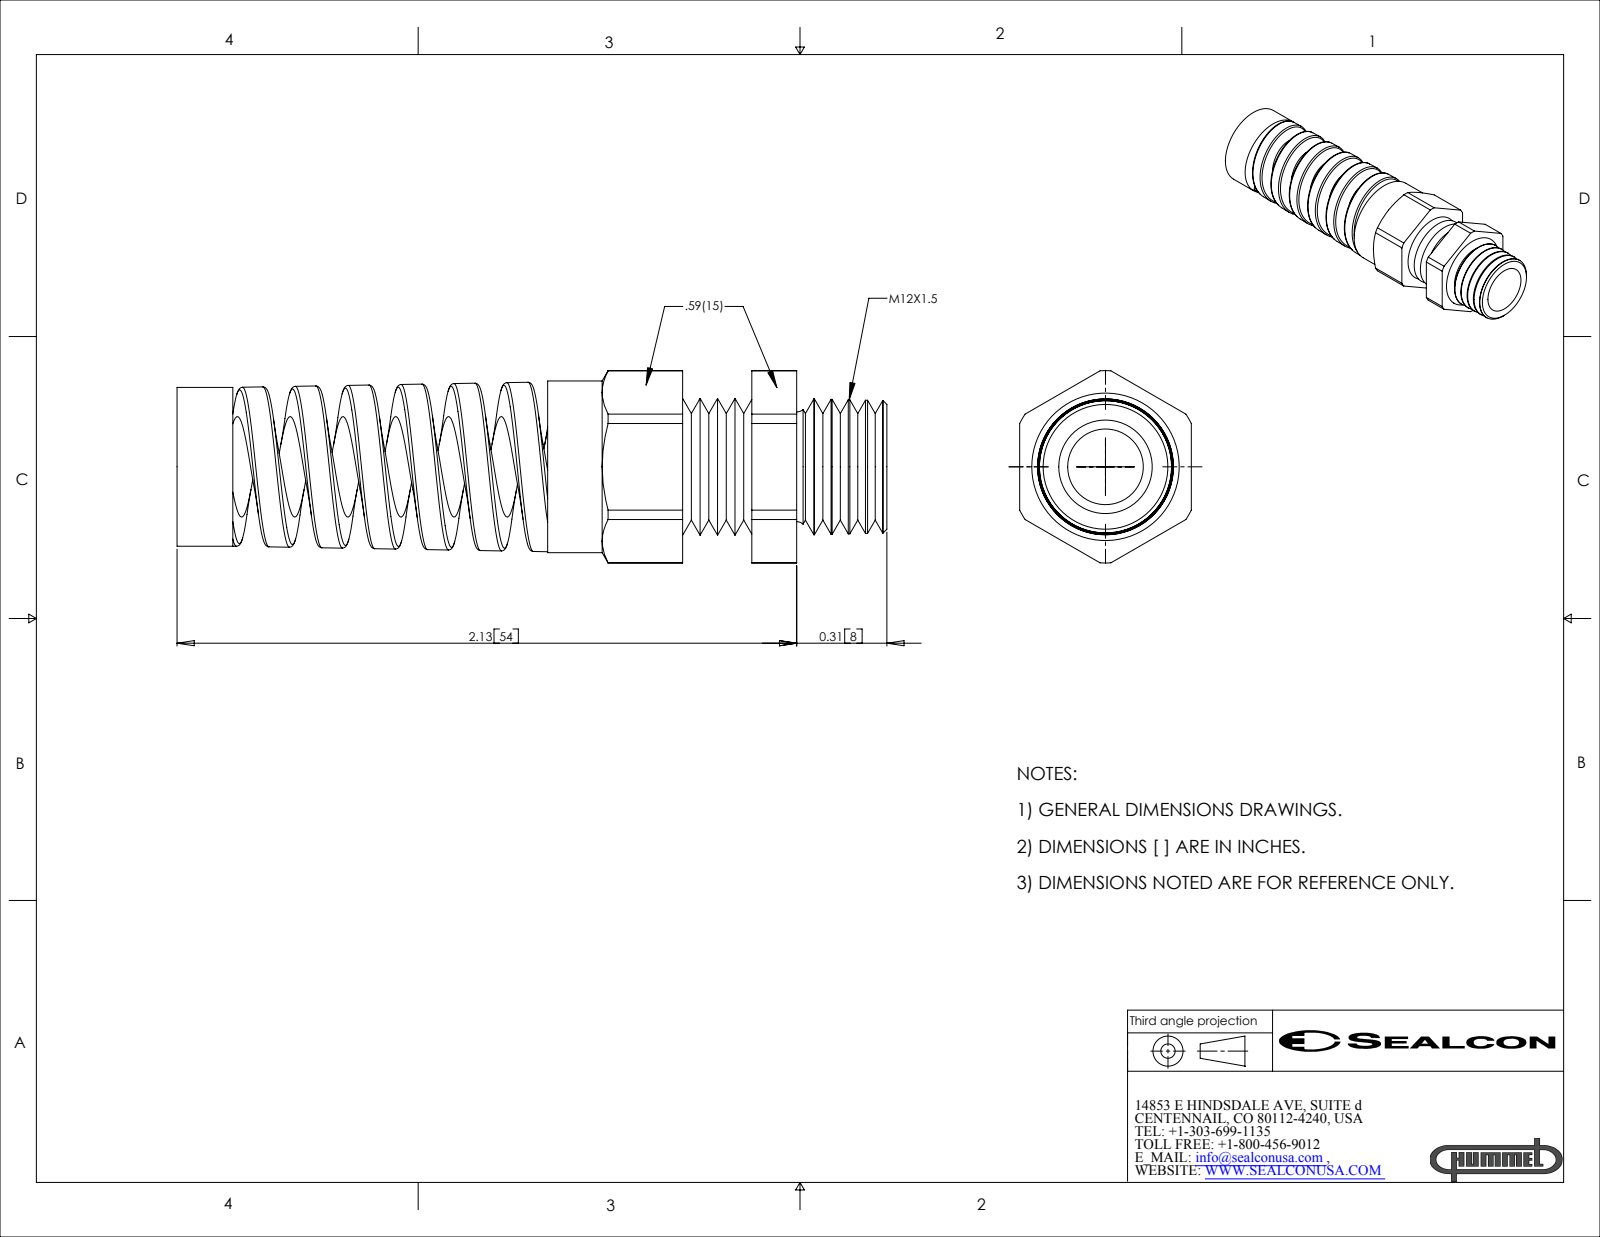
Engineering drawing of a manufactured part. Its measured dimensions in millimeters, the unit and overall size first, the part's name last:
Units: millimetres
Overall size (bounding box): 62 × 16.8 × 15
Round holes (diameter × count): ⌀6.6 ×1, ⌀8.8 ×1, ⌀11.9 ×1
Round bosses / shafts (diameter × count): ⌀15 ×1, ⌀13.9 ×1
Partial cylindrical surfaces — rounded edges, fillets, slot ends (radius × count): R8.4 ×1
Main face-to-face distances: 15, 50.2, 44.1, 6, 32.4, 11.8, 17.8, 54.1, 21.7, 10
Volume: 4 920 mm³ · Surface area: 5 494 mm²
Bodies: 1 solid, 131 faces (19 planar, 34 cylindrical, 78 other)
Part name (STEP PRODUCT): CF12MA-GY
STEP written by: SolidWorks 2007 (CONFIG_CONTROL_DESIGN)
